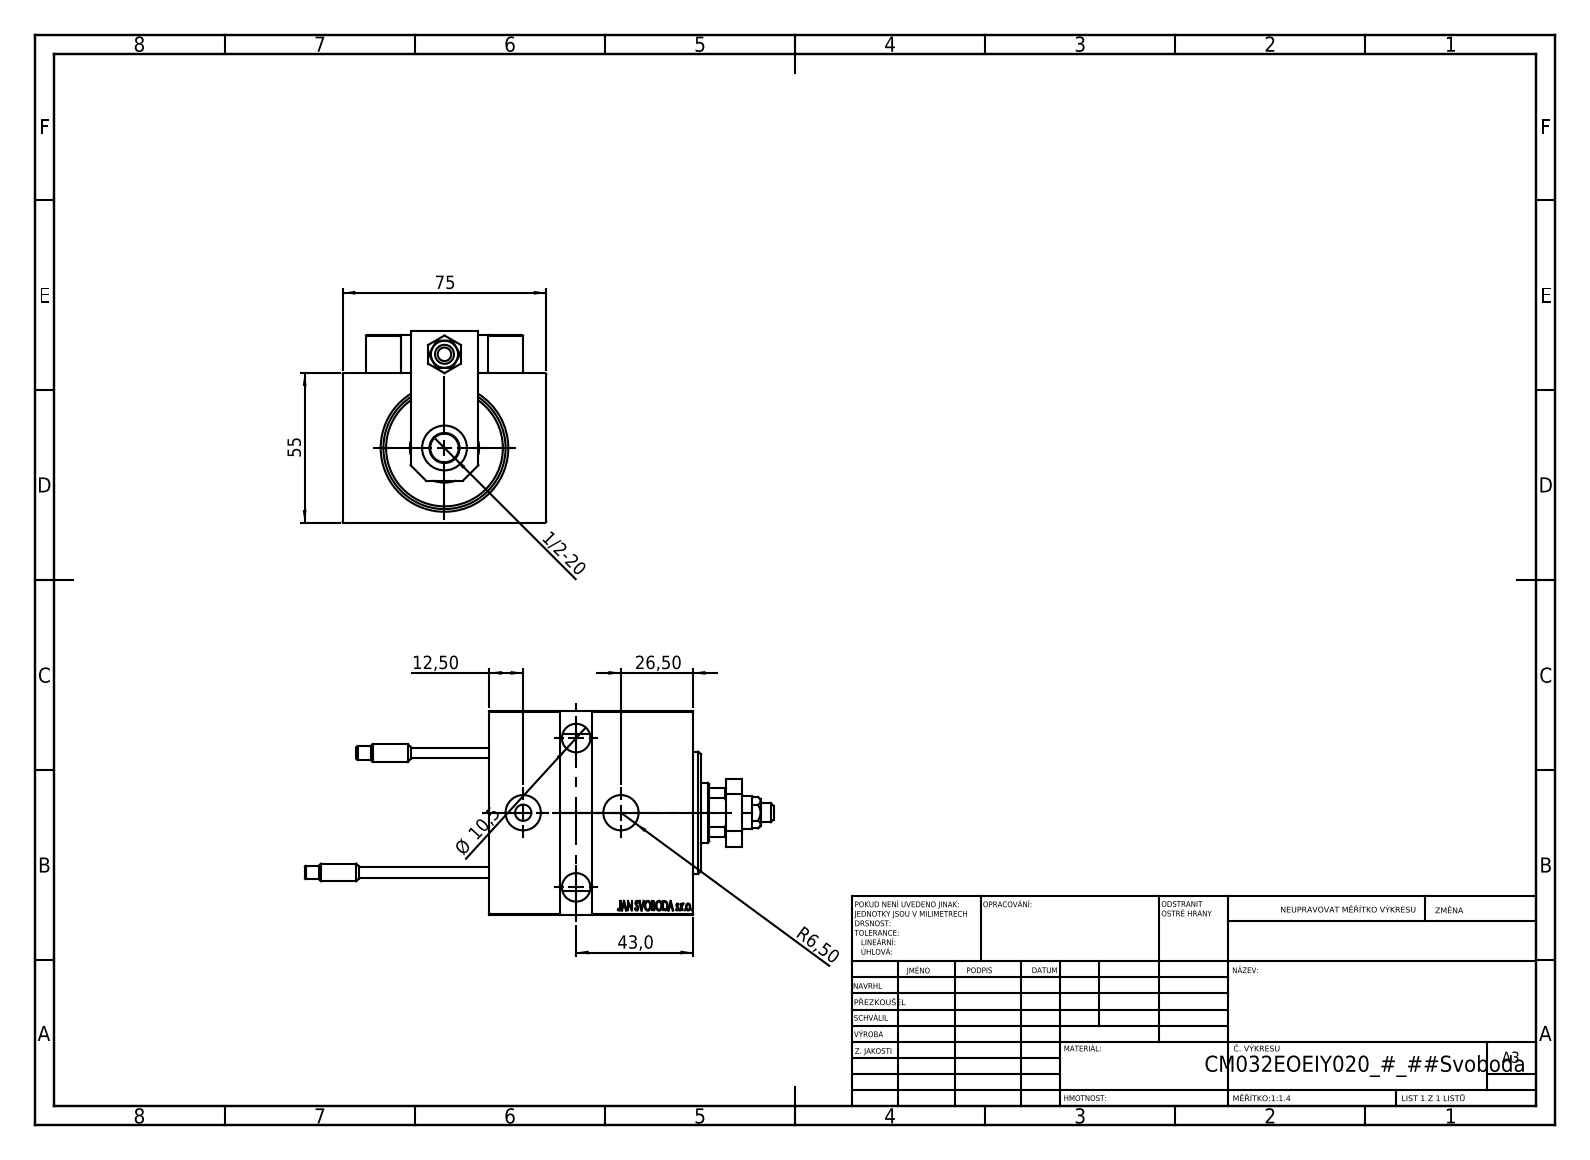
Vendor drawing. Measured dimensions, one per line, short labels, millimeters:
name: SWITCH X; NUT_D10; SWITCH_X_FRONT_BACK; V450CM_VC_B (+8 more)
written by: SolidWorks 2019 (CONFIG_CONTROL_DESIGN)
unit: mm
bodies: 24 solids, 1295 faces (568 planar, 174 cylindrical, 553 other)
size: 172.7 × 75 × 70.5
volume: 338 634 mm³; area: 77 092 mm²
holes: 5× ⌀8, 4× ⌀3.2, 4× ⌀4, 3× ⌀10.5, 3× ⌀16.5, 2× ⌀5, 2× ⌀13, 1× ⌀7, 1× ⌀22, 1× ⌀25.5, 1× ⌀32, 1× ⌀45
bosses: 4× ⌀5, 2× ⌀6.5, 2× ⌀3.8, 1× ⌀34, 1× ⌀13, 1× ⌀11, 1× ⌀6
rounds: 30× R0.3, 2× R3, 1× R10.5
face distances: 75, 55, 3, 10, 12, 14, 65, 25, 7, 5
hole spacings: 11.37, 12.5, 20, 21.91, 27.07, 29.59, 29.69, 32.07
